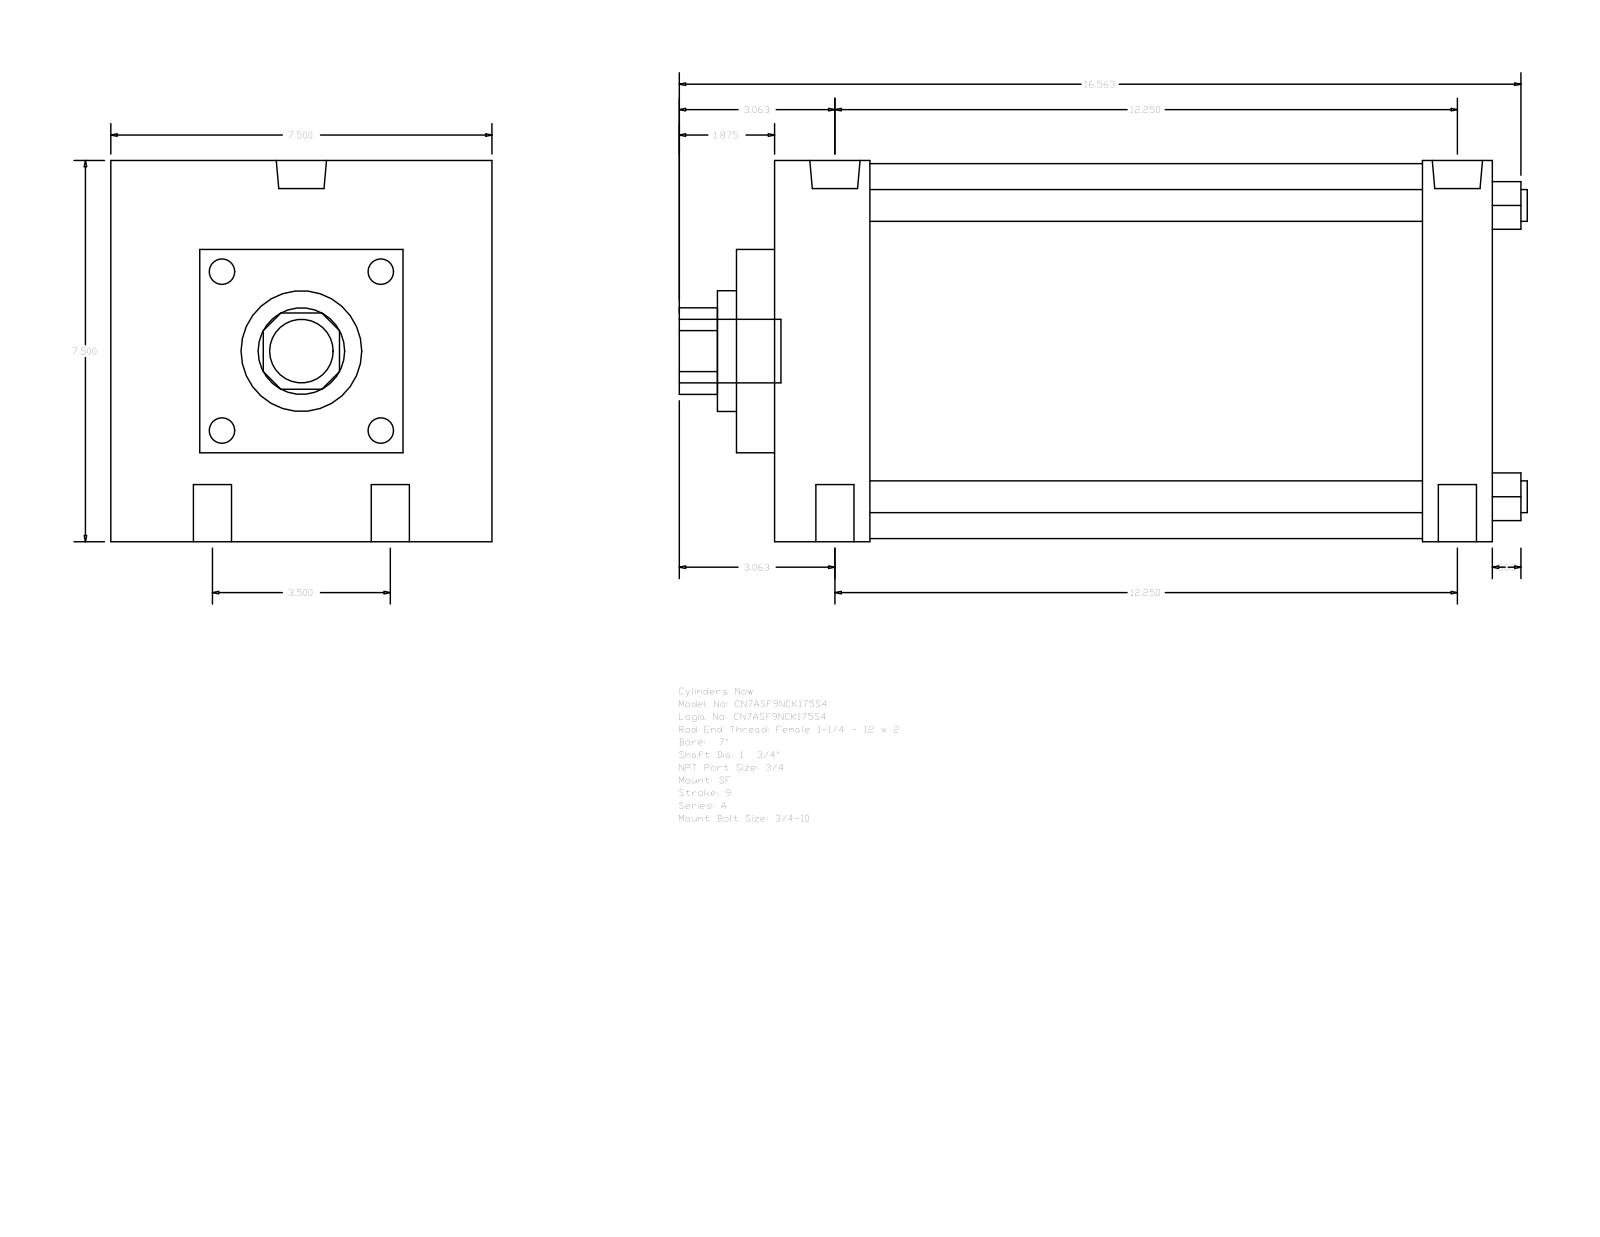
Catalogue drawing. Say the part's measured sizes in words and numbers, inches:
The part is named "A_SF__0700_1.75". Its 3-D file was written by "GSSL Pune (CONFIG_CONTROL_DESIGN)". It is 0 solids with 93 faces: 67 planar, 26 cylindrical and 0 other. Overall it measures 16.687 by 7.5 by 7.5 inches. Round holes: 4 of diameter 0.75, 2 of diameter 0.594, 2 of diameter 0.989, 1 of diameter 1.75, 1 of diameter 2.375. Round bosses or shafts: 4 of diameter 0.625, 1 of diameter 7.375, 1 of diameter 1.25. Partial cylindrical surfaces (rounded edges, fillets, slot ends): 1 of radius 0.852. The main face-to-face distances are 7.5, 14.125, 1.75, 1.375, 0.75, 1.875, 12.75, 10.875, 12.25, 5.75. The hole center spacings are 1.75, 12.374, 12.25, 3.5, 12.74, 11.812.
